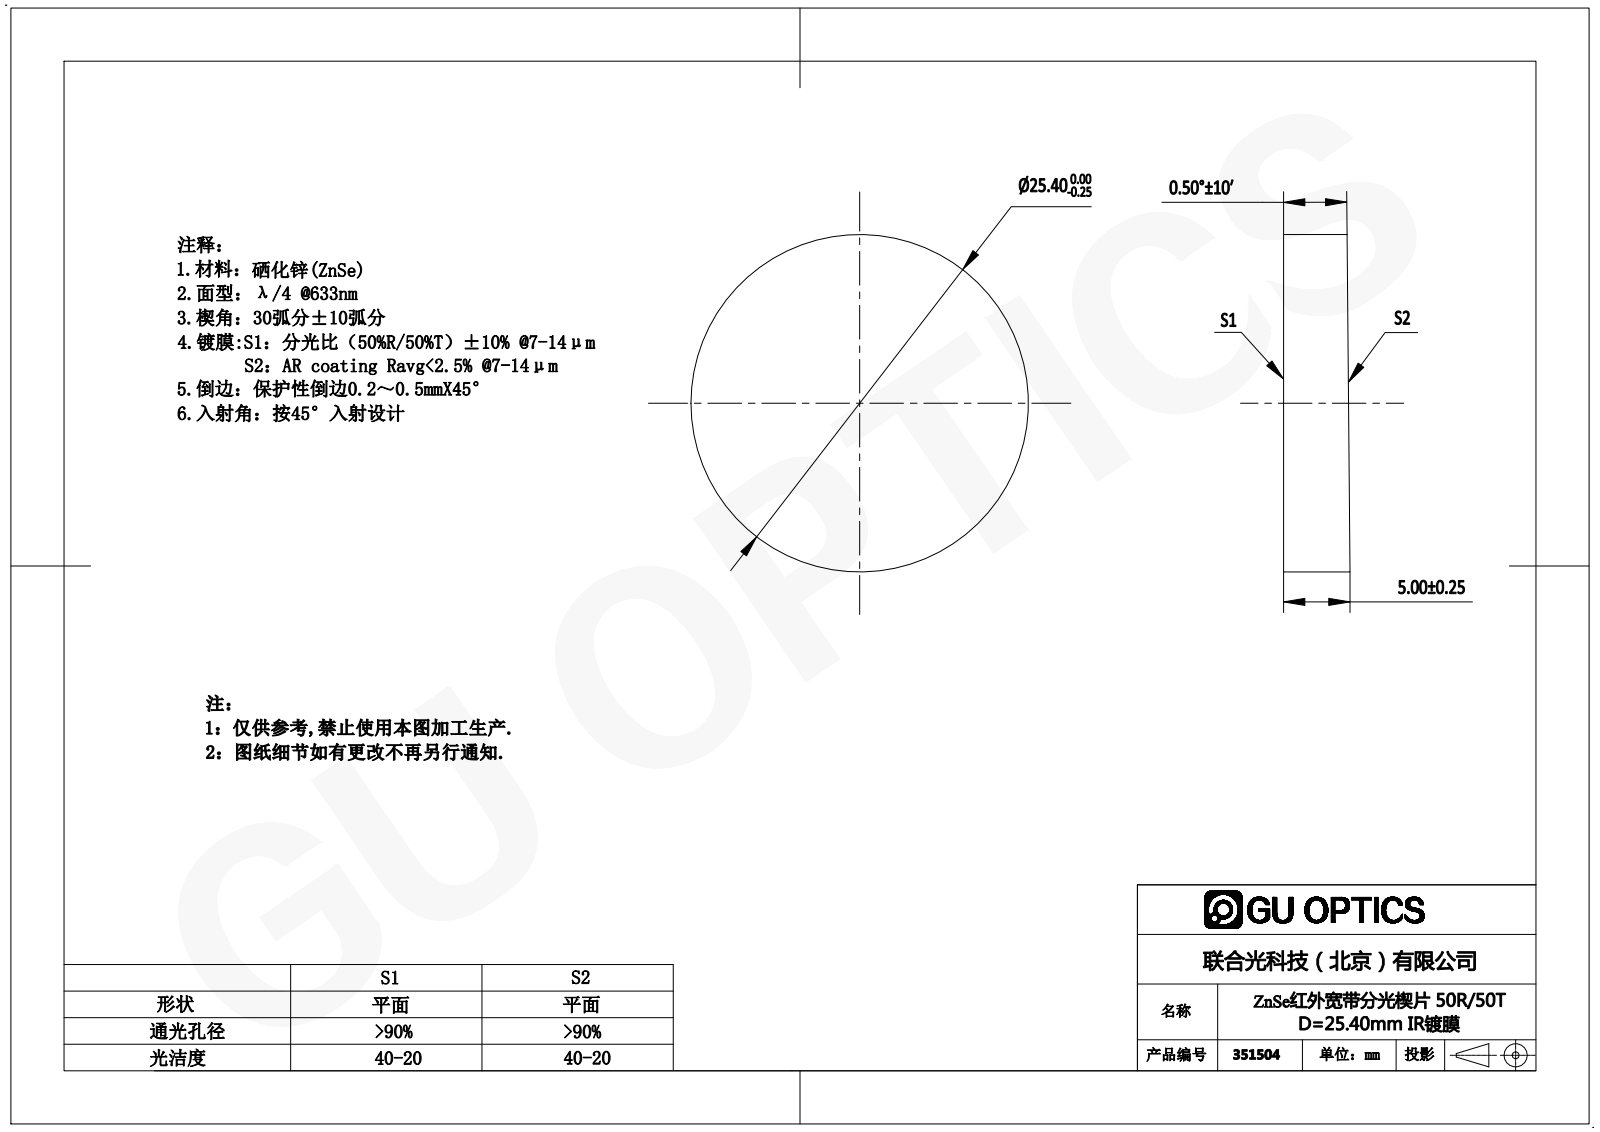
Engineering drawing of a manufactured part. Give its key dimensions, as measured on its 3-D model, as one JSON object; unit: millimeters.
{"part_name": "351501", "step_written_by": "SolidWorks 2016 (AUTOMOTIVE_DESIGN)", "units": "millimeters", "bodies": {"solids": 1, "faces": 4, "planar": 2, "cylindrical": 2, "other": 0}, "overall_size": [25.4, 25.4, 5], "volume_mm3": 2477, "surface_area_mm2": 1404, "round_bosses_or_shafts": [[25.4, 1]]}
